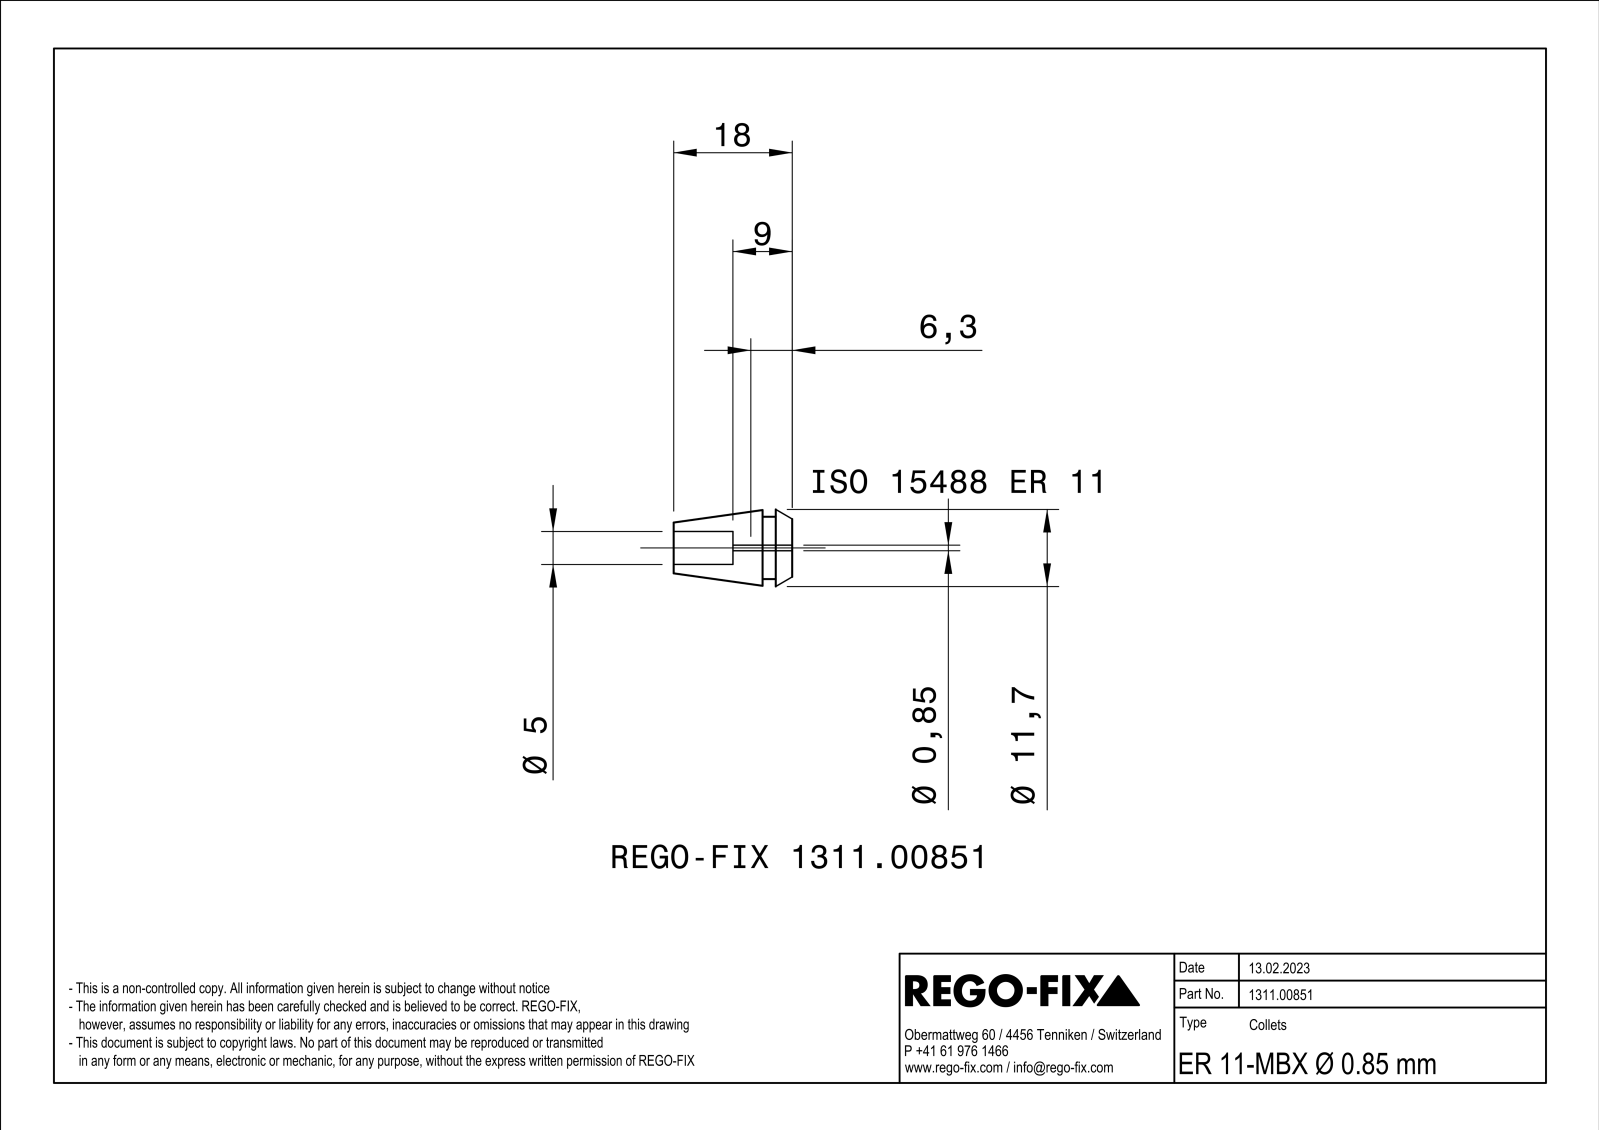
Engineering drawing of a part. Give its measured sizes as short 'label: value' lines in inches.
name: NOCUT
written by: SIEMENS PLM Software Solid Edge ST10 (AUTOMOTIVE_DESIGN)
unit: in
bodies: 1 solid, 91 faces (26 planar, 19 cylindrical, 46 other)
size: 0.709 × 0.449 × 0.448
volume: 0.06 in³; area: 1.942 in²
holes: 3× ⌀0.059, 1× ⌀0.197
bosses: 1× ⌀0.374
rounds: 3× R0.984, 1× R0.017
face distances: 0.031, 0.177, 0.021, 0.354, 0.709, 0.531, 0.098, 0.079, 0.61, 0.256
hole spacings: 0.067, 0.116
